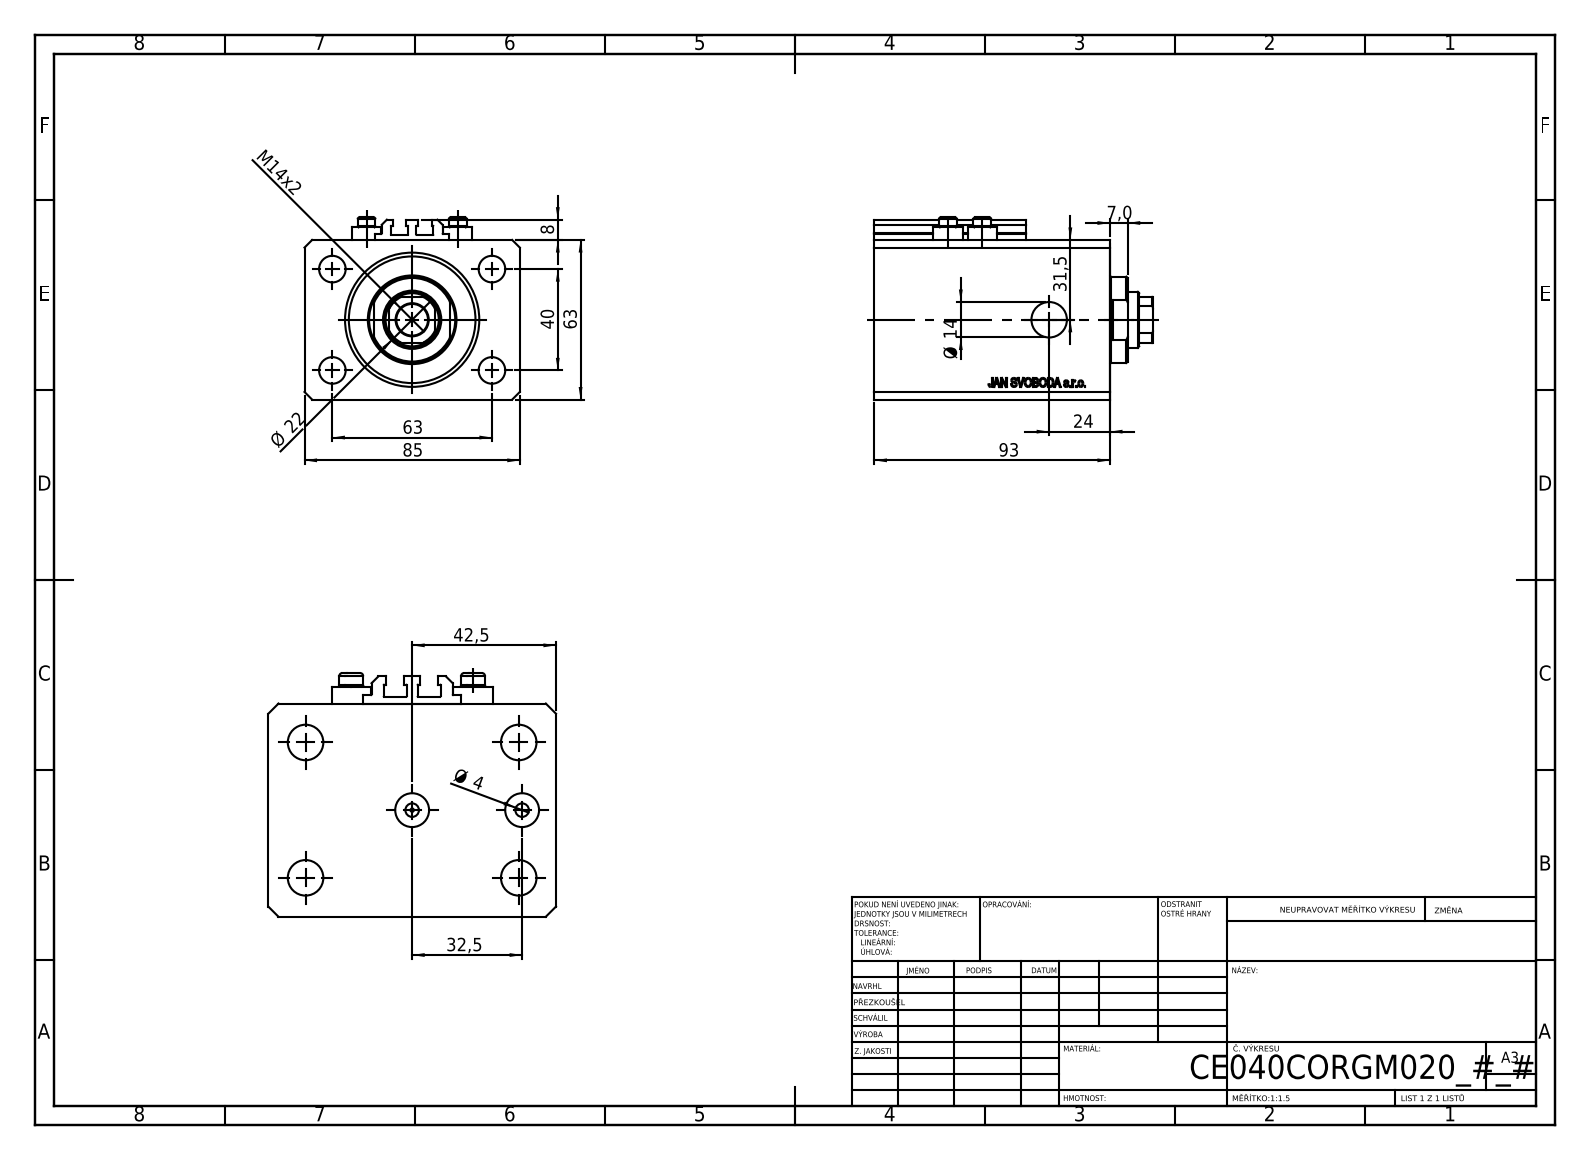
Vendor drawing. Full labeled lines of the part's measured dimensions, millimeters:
Part name (STEP PRODUCT): ALLEN BOLT V250CE; V250CE_C_VCP; V250CE_VC_C; V250CE_C_Body
STEP written by: SolidWorks 2019 (CONFIG_CONTROL_DESIGN)
Units: millimetres
Bodies: 8 solids, 1036 faces (504 planar, 86 cylindrical, 446 other)
Overall size (bounding box): 110 × 85 × 72
Volume: 459 881 mm³ · Surface area: 92 481 mm²
Round holes (diameter × count): ⌀4 ×7, ⌀10.5 ×4, ⌀10 ×2, ⌀14 ×2, ⌀1.25 ×1, ⌀12.5 ×1, ⌀22 ×1, ⌀40 ×1, ⌀53 ×1
Round bosses / shafts (diameter × count): ⌀11.6 ×4, ⌀7 ×4, ⌀34 ×1
Partial cylindrical surfaces — rounded edges, fillets, slot ends (radius × count): R0.2 ×10, R10.5 ×1
Main face-to-face distances: 63, 85, 93, 17, 76, 11.4, 64.6, 81.6, 3, 10
Hole centre spacings: 37.31, 13.6, 20.02, 36, 38.48, 40, 63, 67.05
